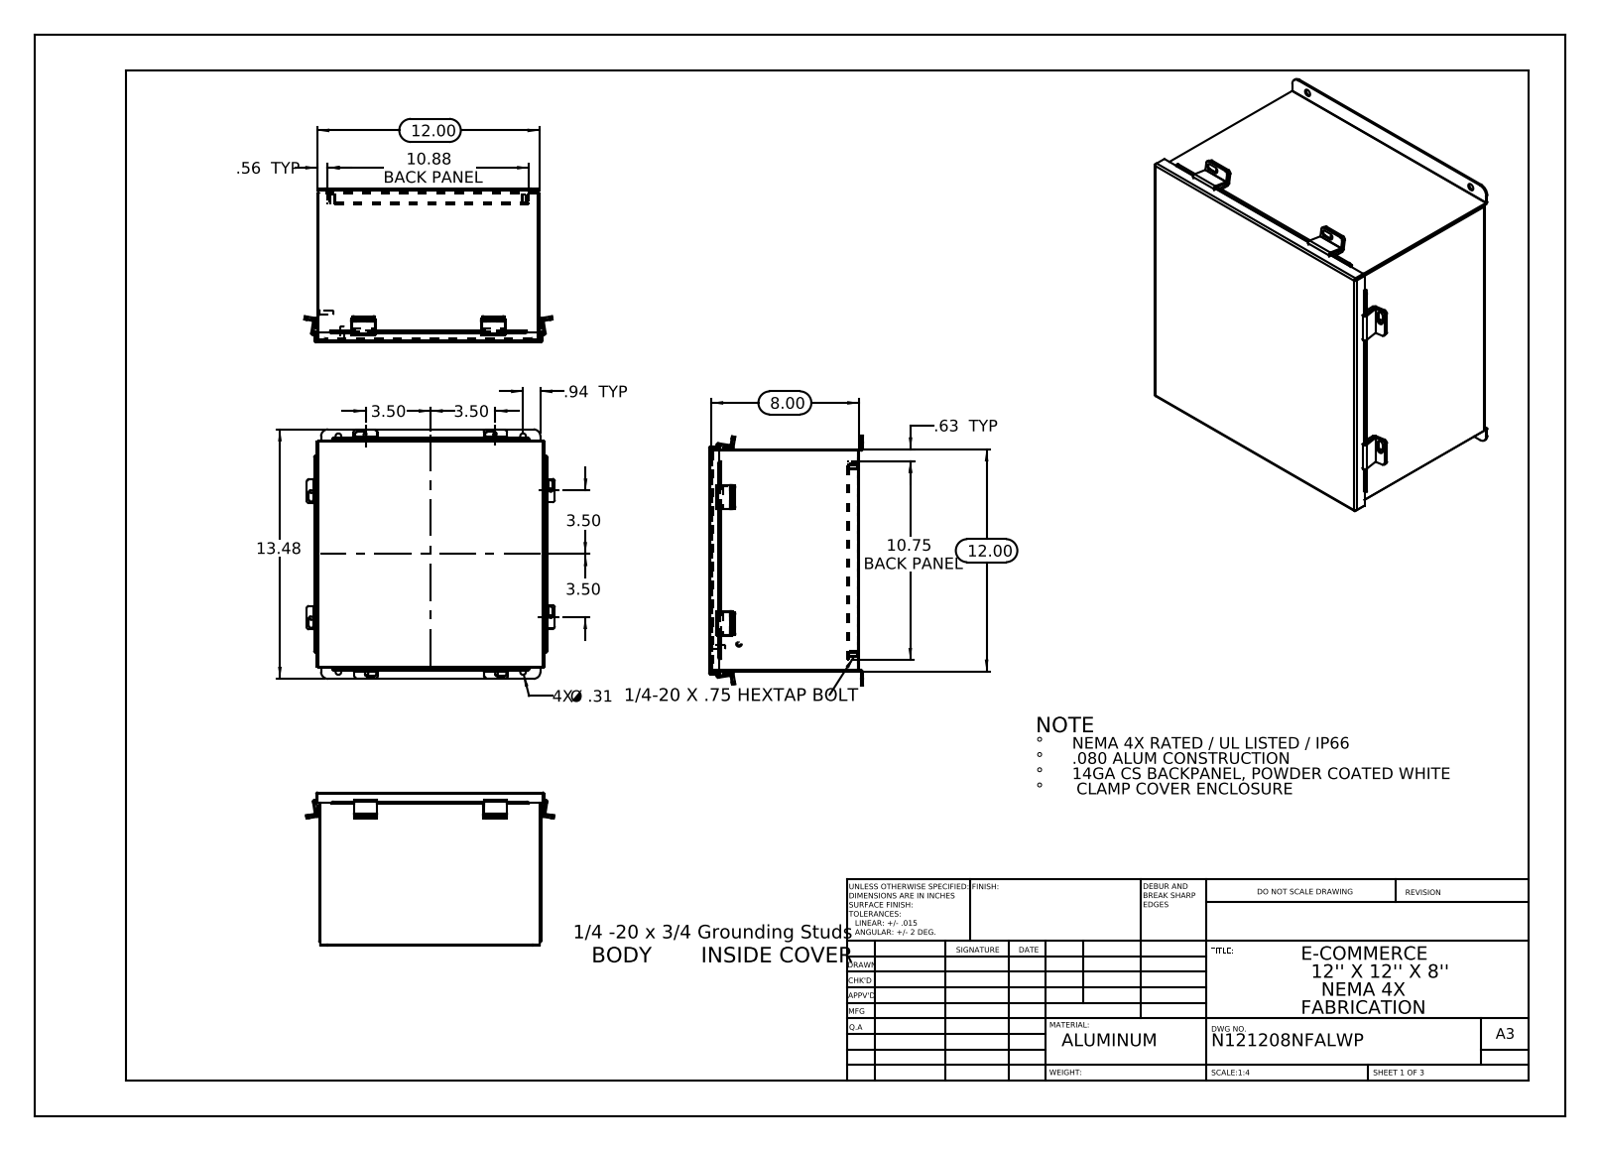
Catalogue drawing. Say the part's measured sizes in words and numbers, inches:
The part is named "N121208NFSSWP JIC Top; N121208NFSSWP JIC_Cover_Template; HW-CLH-JH-20154; N121208NFSSWP JIC Cover Clamp (+8 more)". Its 3-D file was written by "SolidWorks 2013 (CONFIG_CONTROL_DESIGN)". It is 27 solids with 774 faces: 499 planar, 255 cylindrical and 20 other. Overall it measures 13.476 by 13.072 by 8.39 inches. Its volume is 67.03 cubic inches and its surface area 1 825 square inches. Round holes: 10 of diameter 0.25, 4 of diameter 0.187, 4 of diameter 0.312, 1 of diameter 0.125, 1 of diameter 0.125, 1 of diameter 0.373, 1 of diameter 0.375. Round bosses or shafts: 4 of diameter 0.313, 2 of diameter 0.315, 2 of diameter 0.236, 1 of diameter 0.273, 1 of diameter 0.25. Partial cylindrical surfaces (rounded edges, fillets, slot ends): 21 of radius 0.125, 13 of radius 0.013, 12 of radius 0.009, 12 of radius 0.088, 12 of radius 0.133, 6 of radius 0.083, 6 of radius 0.1, 4 of radius 0.375. The main face-to-face distances are 0.075, 11.925, 8.128, 11.85, 12, 8.053, 8.203, 0.074, 0.575, 0.5. The hole center spacings are 1.315, 10.258, 11.428, 15.3, 7, 9.976, 10.126, 10.375.
